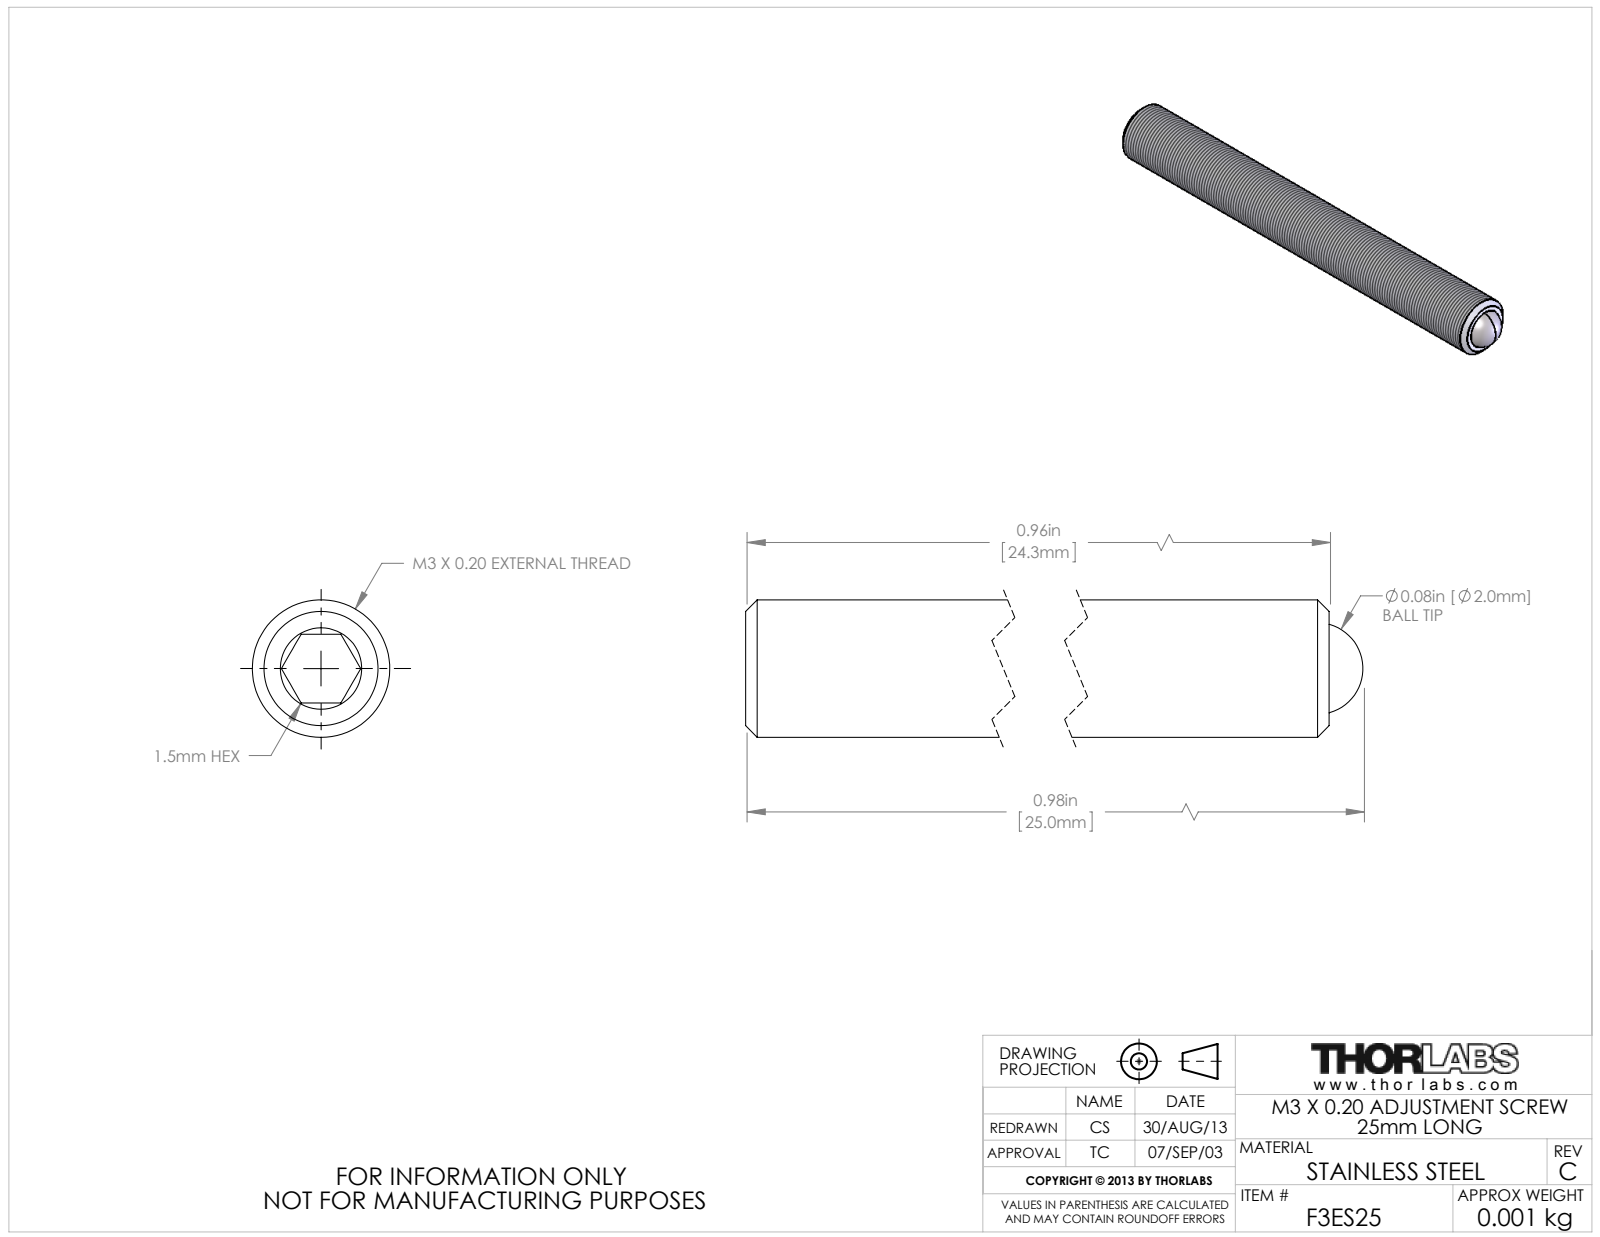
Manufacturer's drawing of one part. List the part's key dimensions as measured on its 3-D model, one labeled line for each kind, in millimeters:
Part name (STEP PRODUCT): 8568-E0W
STEP written by: SolidWorks 2012 (AUTOMOTIVE_DESIGN)
Units: millimetres
Bodies: 2 solids, 25 faces (9 planar, 4 cylindrical, 12 other)
Overall size (bounding box): 25 × 3 × 3
Volume: 160 mm³ · Surface area: 274 mm²
Round holes (diameter × count): ⌀2 ×1
Round bosses / shafts (diameter × count): ⌀3 ×1
Main face-to-face distances: 1.5, 3, 21.2, 24.3
